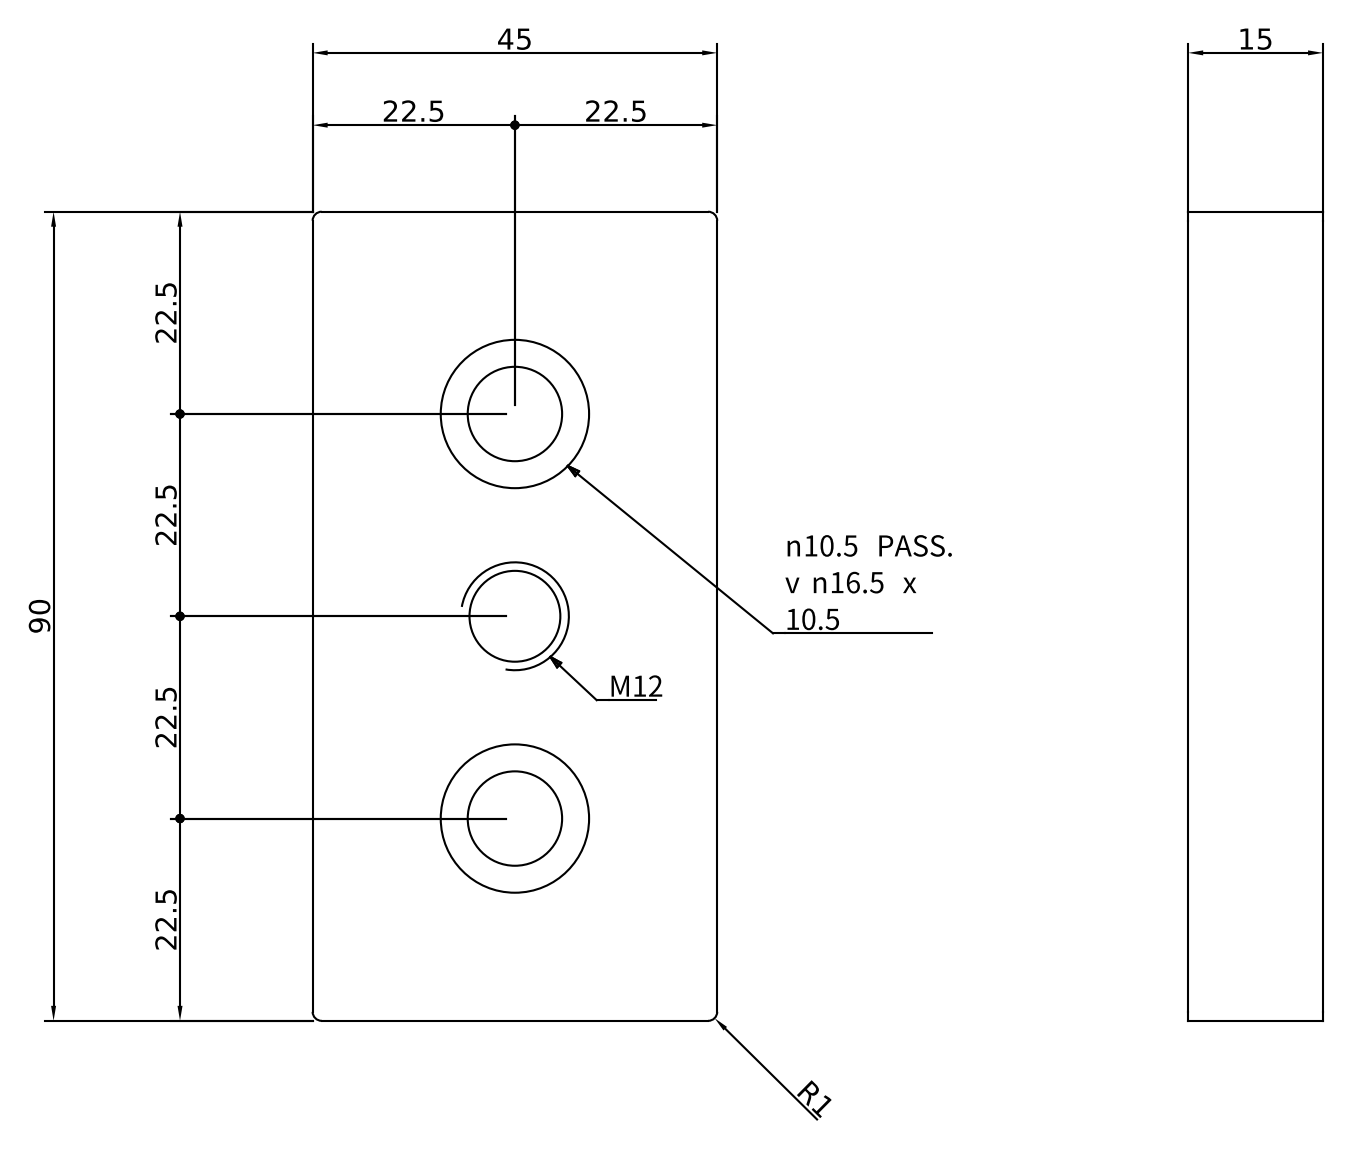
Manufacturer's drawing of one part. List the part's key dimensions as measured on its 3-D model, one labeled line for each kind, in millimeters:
Part name (STEP PRODUCT): 440000006754
STEP written by: Autodesk Inventor 2016 (AUTOMOTIVE_DESIGN)
Units: millimetres
Bodies: 1 solid, 17 faces (8 planar, 9 cylindrical, 0 other)
Overall size (bounding box): 90 × 45 × 10
Volume: 37 017 mm³ · Surface area: 11 464 mm²
Round holes (diameter × count): ⌀8.5 ×2, ⌀13.5 ×2, ⌀10.11 ×1
Partial cylindrical surfaces — rounded edges, fillets, slot ends (radius × count): R3 ×4
Main face-to-face distances: 10, 45, 90, 1.5, 8.5
Hole centre spacings: 22.5, 45
